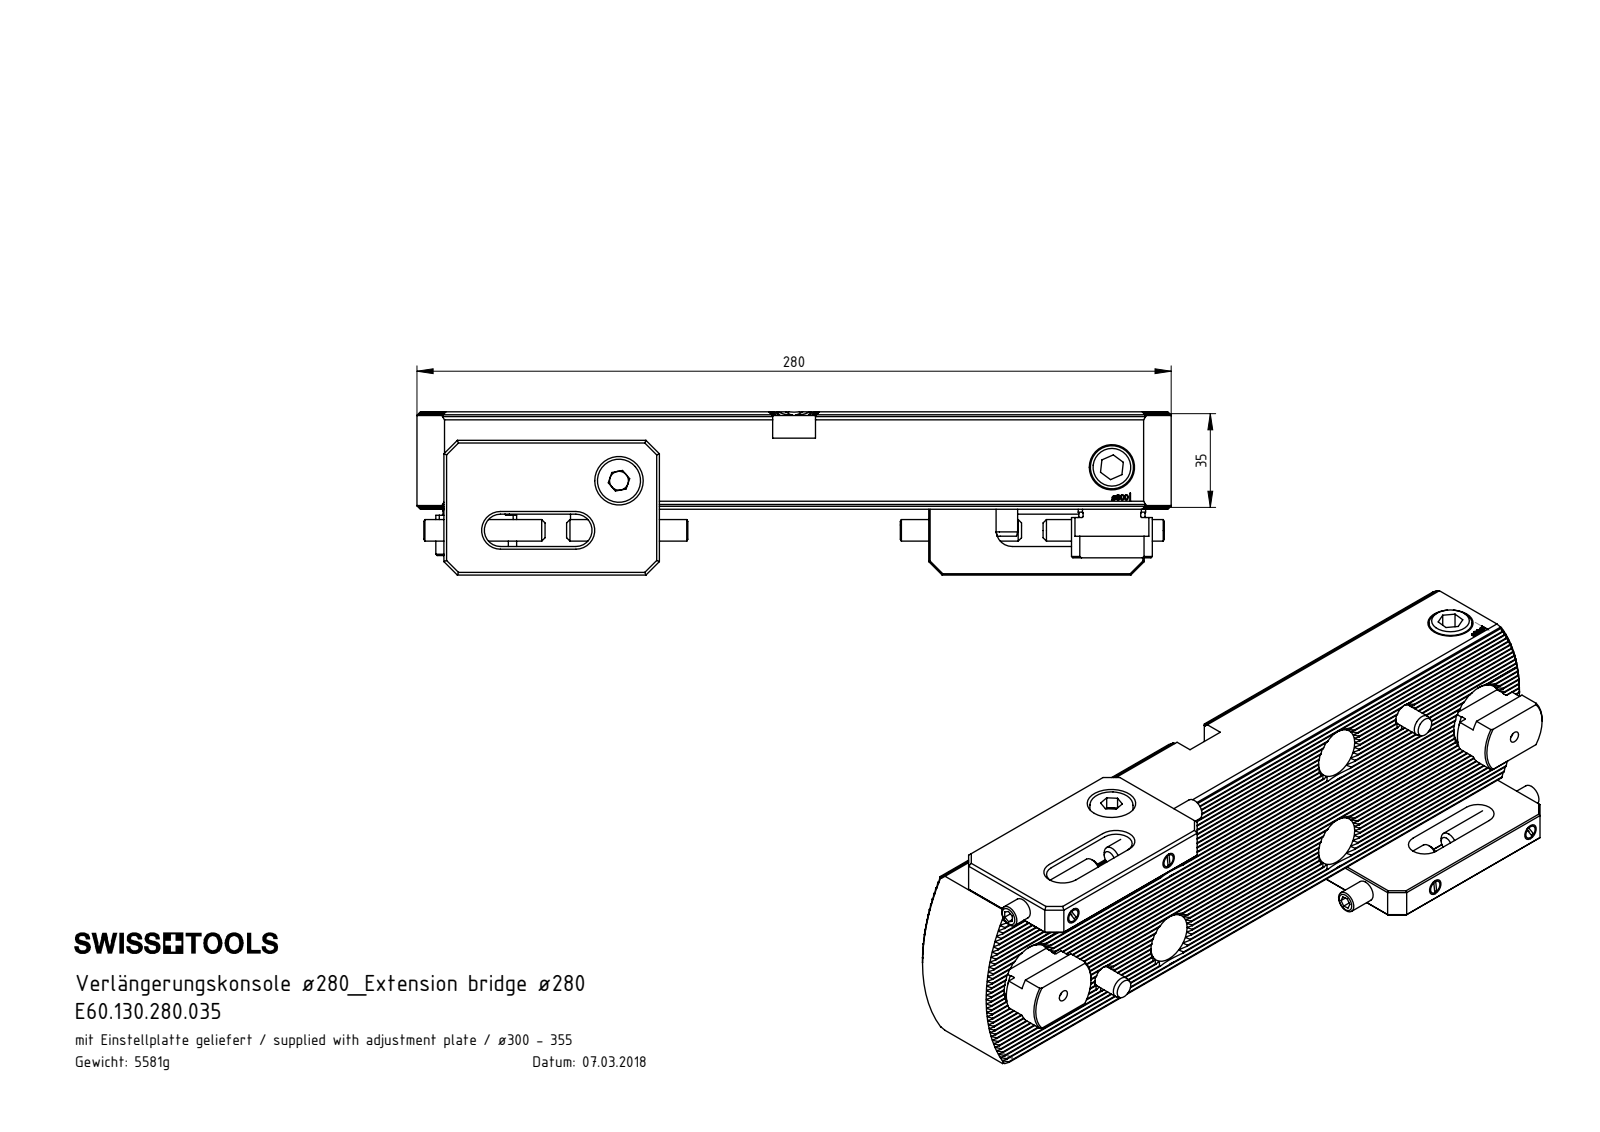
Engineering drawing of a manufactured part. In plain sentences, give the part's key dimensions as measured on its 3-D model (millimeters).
The part is named "VK1-ER7.001.012_mit langer Schraube; ISO 4766 - M6x12_ISO 4766 - M6 x 10; DIN 7984 - M10 x 16; ISO 4026 - M8 x 45 (+8 more)". Its 3-D file was written by "SolidWorks 2017 (CONFIG_CONTROL_DESIGN)". It is 27 solids with 1787 faces: 975 planar, 477 cylindrical and 335 other. Overall it measures 280 by 94 by 60.58 millimeters. Its volume is 716 990 cubic millimeters and its surface area 152 062 square millimeters. Round holes: 4 of diameter 5, 4 of diameter 6, 4 of diameter 6.8, 4 of diameter 13, 4 of diameter 19, 2 of diameter 2, 2 of diameter 8, 2 of diameter 8.5, 2 of diameter 10.5, 2 of diameter 11, 2 of diameter 14, 2 of diameter 18. Round bosses or shafts: 4 of diameter 16, 4 of diameter 6, 2 of diameter 10, 2 of diameter 8. Partial cylindrical surfaces (rounded edges, fillets, slot ends): 66 of radius 0.14, 8 of radius 2, 4 of radius 6, 2 of radius 12.3, 2 of radius 15, 2 of radius 65, 1 of radius 7.95. The main face-to-face distances are 70, 1.73, 12, 82, 16.64, 3.46, 51.96, 0.5, 11.5, 82.5. The hole center spacings are 76.66, 163.23, 236, 7.9, 18.55, 19.61, 33.42, 34.53.
